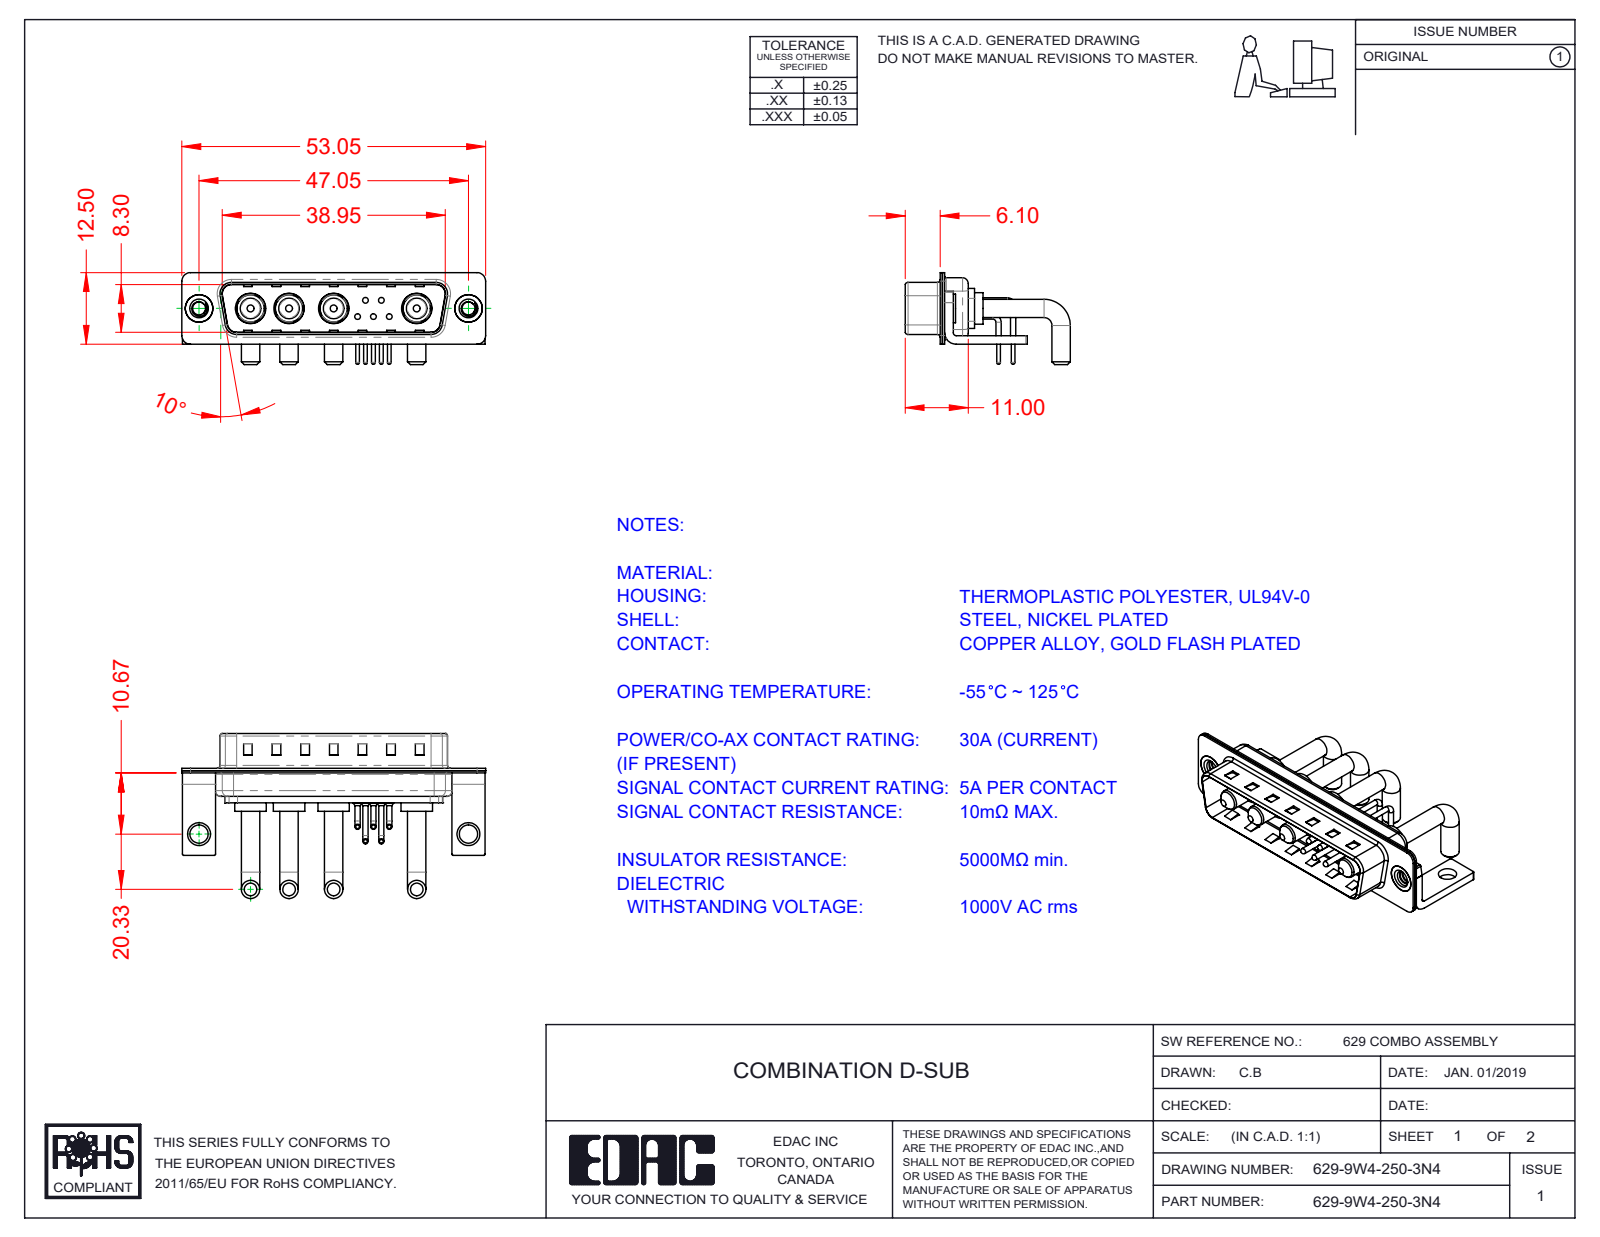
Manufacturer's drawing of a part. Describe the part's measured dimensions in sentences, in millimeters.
The part is named "629Combo Contact Row 1; 629Combo Shell Rear_25 Contacts; 629Combo Housing_9W4; 629Combo Threaded Rivet_3 (+5 more)". Its 3-D file was written by "SolidWorks 2020 (CONFIG_CONTROL_DESIGN)". It is 20 solids with 1138 faces: 551 planar, 419 cylindrical and 168 other. Overall it measures 53.05 by 28.83 by 16.05 millimeters. Its volume is 3 913 cubic millimeters and its surface area 8 198 square millimeters. Round holes: 5 of diameter 0.75, 5 of diameter 1.6, 5 of diameter 2, 4 of diameter 4.85, 4 of diameter 5.3, 2 of diameter 2.26, 2 of diameter 3.2, 2 of diameter 4, 2 of diameter 4.8. Round bosses or shafts: 10 of diameter 0.9, 8 of diameter 3.2, 5 of diameter 1.5, 5 of diameter 1, 5 of diameter 0.65, 4 of diameter 5.5, 4 of diameter 5.2, 4 of diameter 4.75. Partial cylindrical surfaces (rounded edges, fillets, slot ends): 16 of radius 0.25, 16 of radius 1.5, 13 of radius 2, 9 of radius 0.5, 8 of radius 1.6, 5 of radius 1.01, 4 of radius 0.6, 4 of radius 0.65. The main face-to-face distances are 0.4, 0.8, 9.5, 1.5, 9.1, 8.7, 9.9, 5.2, 0.75, 1.2. The hole center spacings are 3.16, 2.77, 5.04, 14.5, 47.05, 2.78, 4.4, 4.41.
